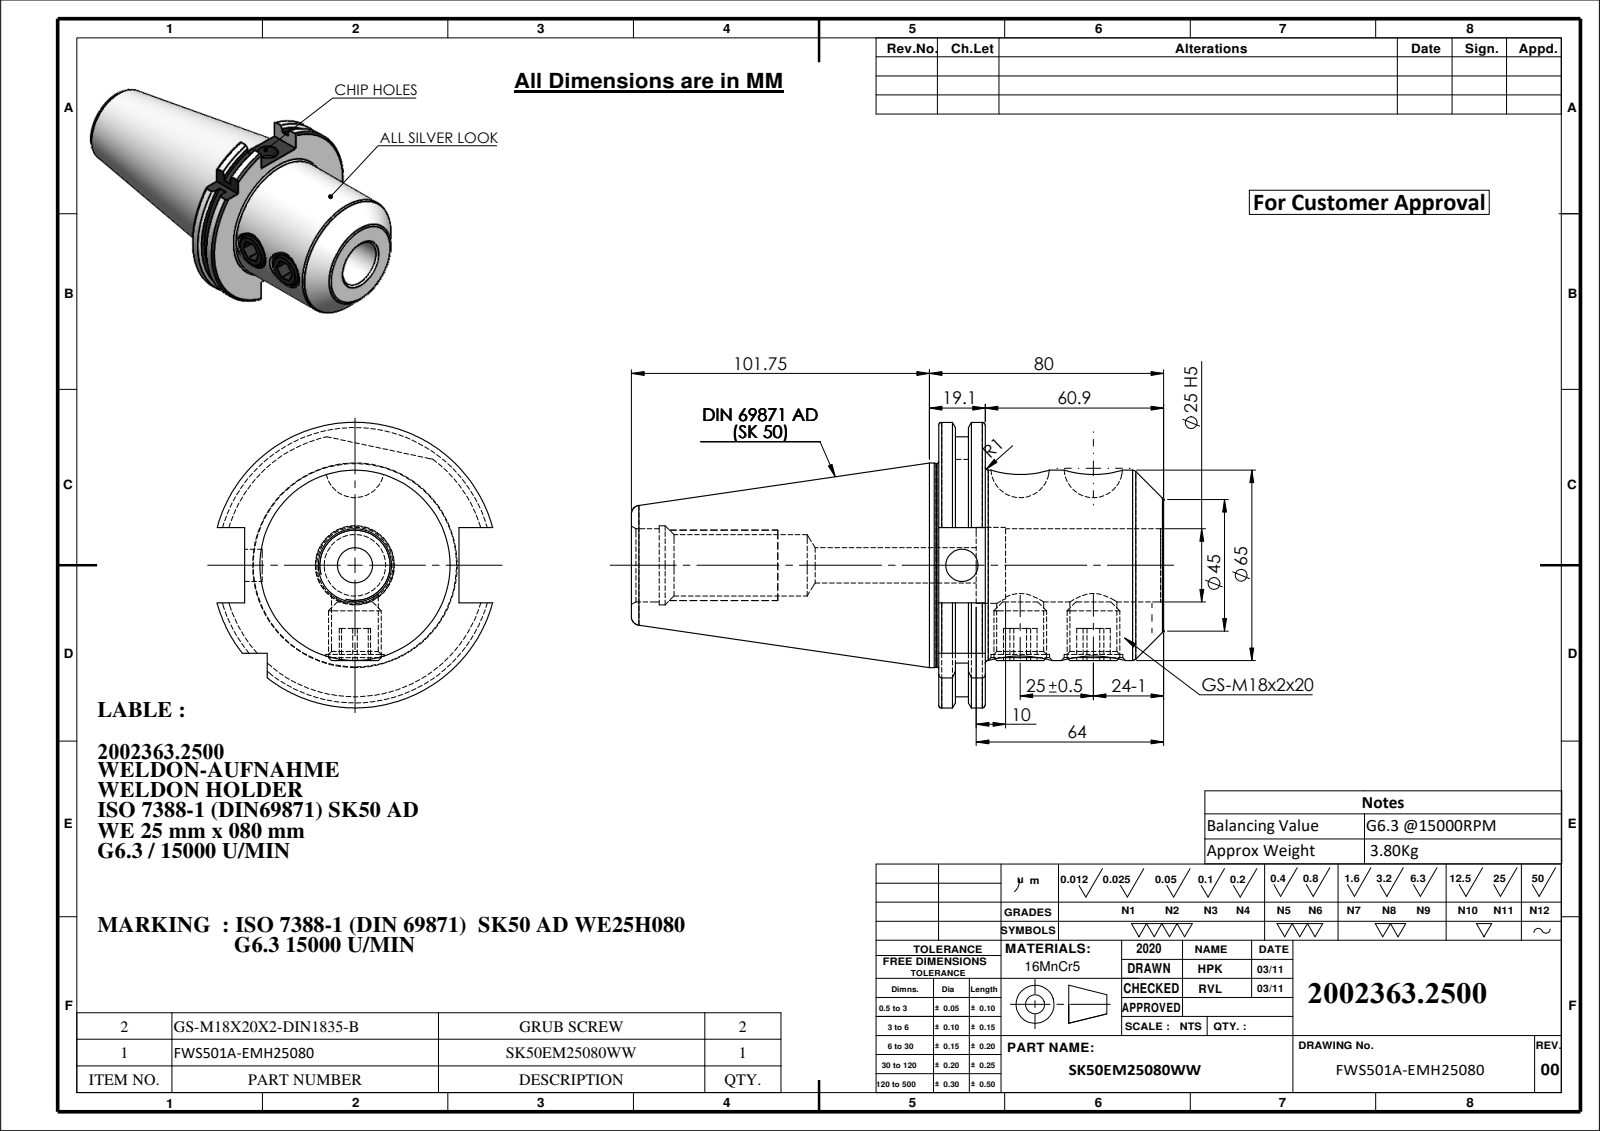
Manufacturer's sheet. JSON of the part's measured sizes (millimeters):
{"part_name": "FWS501A-EMH25080; SK50EM25080WW_ISO; GS-M18X20X2-DIN1835-B; SK50EM25080WW", "step_written_by": "SolidWorks 2024 (CONFIG_CONTROL_DESIGN)", "units": "millimeters", "bodies": {"solids": 3, "faces": 153, "planar": 44, "cylindrical": 45, "other": 64}, "overall_size": [181.75, 97.5, 94.05], "volume_mm3": 489726, "surface_area_mm2": 63980, "round_holes": [[16, 2], [20, 2], [11, 1], [12, 1], [21, 1], [25, 1], [26, 1], [27, 1]], "round_bosses_or_shafts": [[18, 2], [69.85, 1], [69.45, 1], [65, 1]], "partial_cylinders_radius": [[44.9, 1], [48.75, 1]], "face_to_face_distances": [15.9, 76.8, 60.9, 5.66, 10.24, 71.14, 10.14, 4.48, 5.76, 66.66], "hole_center_spacings": [25]}
